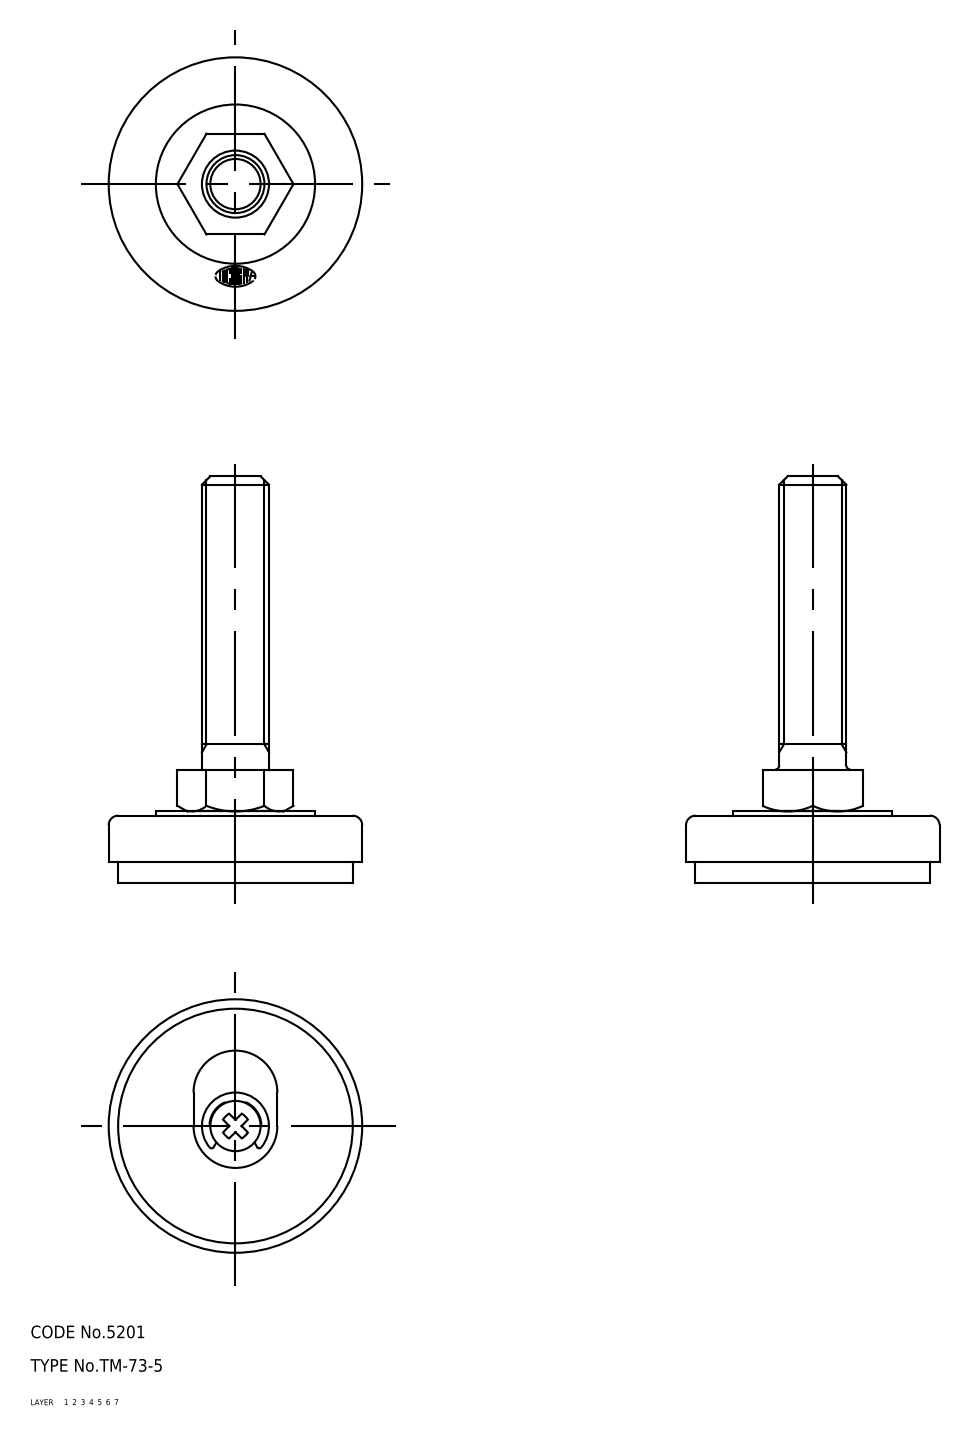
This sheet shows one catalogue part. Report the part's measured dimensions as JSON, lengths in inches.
{"part_name": "washer; rubber pad; retainer; cover (+3 more)", "step_written_by": "CADfix (AUTOMOTIVE_DESIGN)", "units": "inches", "bodies": {"solids": 6, "faces": 119, "planar": 0, "cylindrical": 0, "other": 119}, "overall_size": [3.819, 2.382, 2.382], "volume_in3": 3.7, "surface_area_in2": 49.01}
